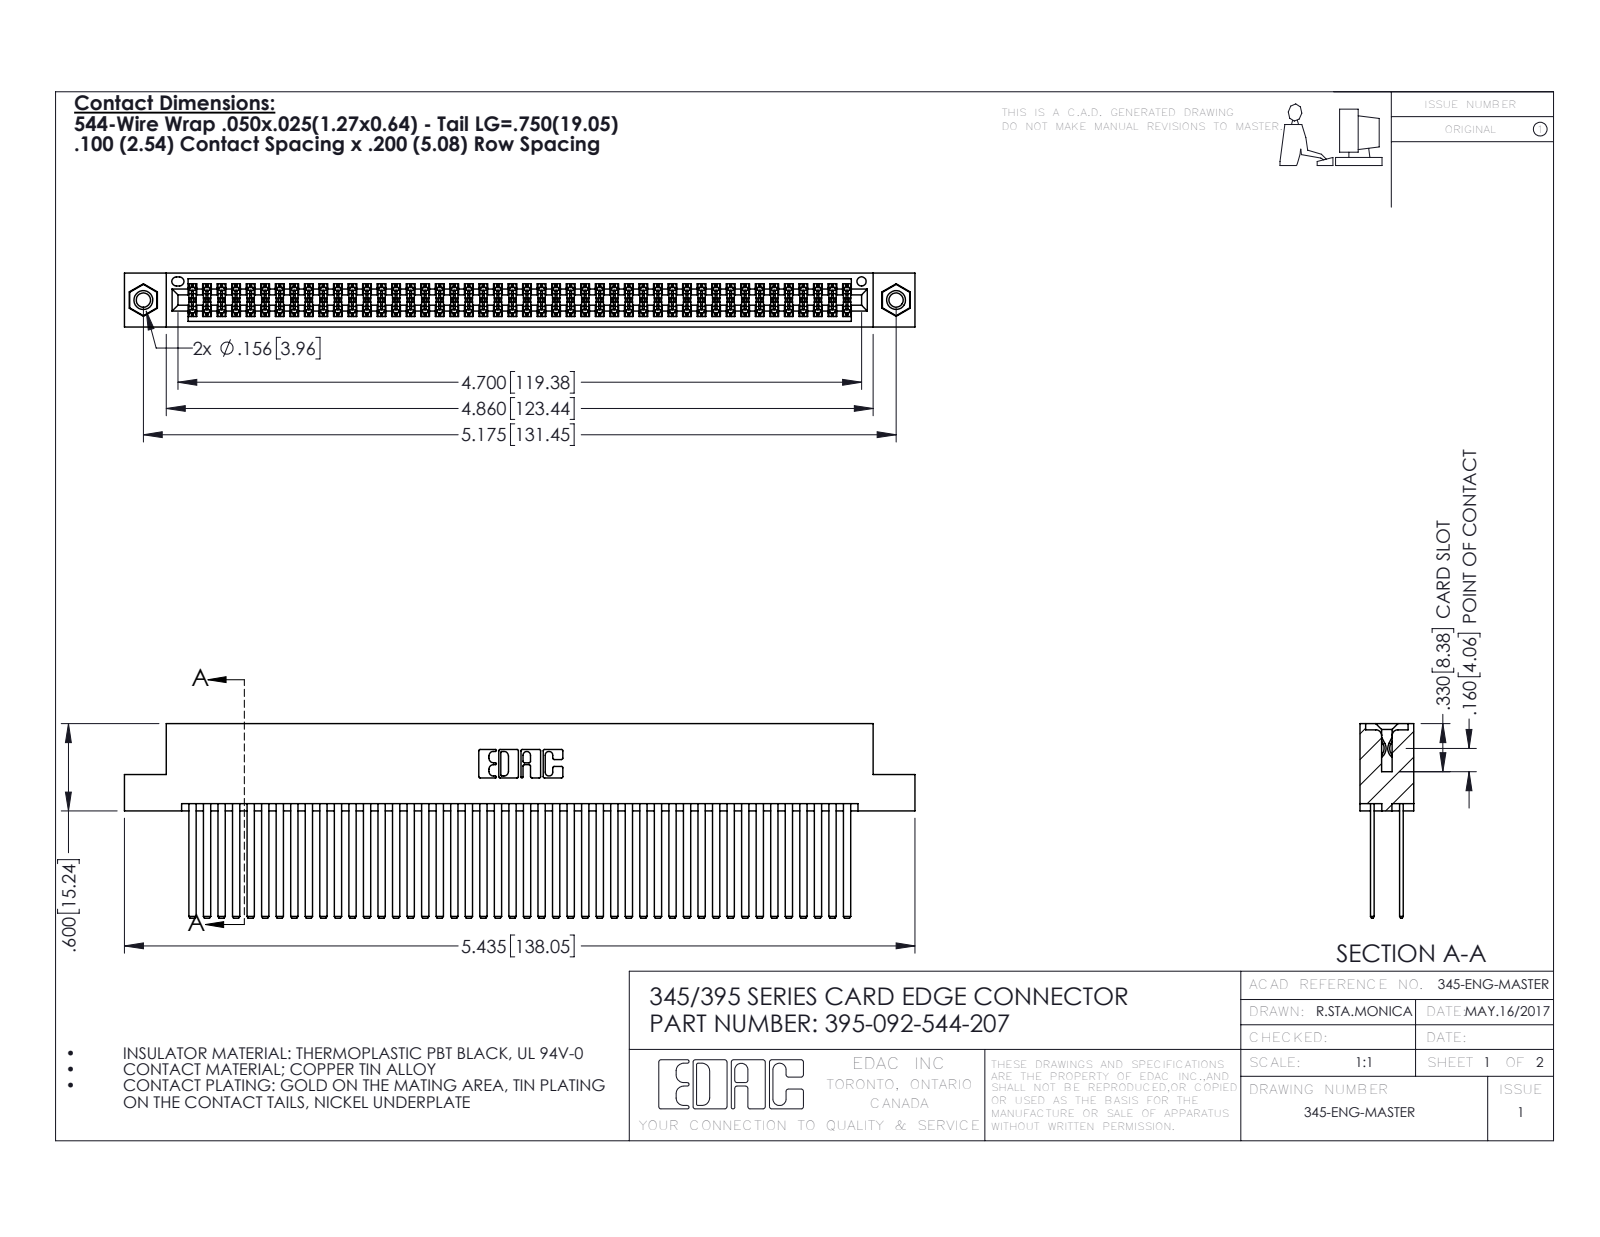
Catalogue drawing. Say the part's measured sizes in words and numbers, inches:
The part is named "345-292-001_345-293-144; 395-092-544-207; 345-250-001_345-250-005-103; 345 Part_Flush Mounting Lugs - 0.156 Dia-TI". Its 3-D file was written by "SolidWorks 2016 (CONFIG_CONTROL_DESIGN)". It is 95 solids with 4234 faces: 2780 planar, 1438 cylindrical and 16 other. Overall it measures 5.435 by 1.337 by 0.37 inches. Its volume is 0.898 cubic inches and its surface area 39.76 square inches. Round holes: 2 of diameter 0.098, 2 of diameter 0.125, 2 of diameter 0.156, 1 of diameter 0.064. Round bosses or shafts: 2 of diameter 0.155. Partial cylindrical surfaces (rounded edges, fillets, slot ends): 138 of radius 0.006, 22 of radius 0.01, 6 of radius 0.007, 6 of radius 0.031, 3 of radius 0.026, 2 of radius 0.014, 2 of radius 0.019, 2 of radius 0.022. The main face-to-face distances are 0.2, 0.025, 0.072, 0.098, 0.272, 0.298, 0.225, 0.175, 0.37, 0.05. The hole center spacings are 0.27, 4.939, 5.175.
